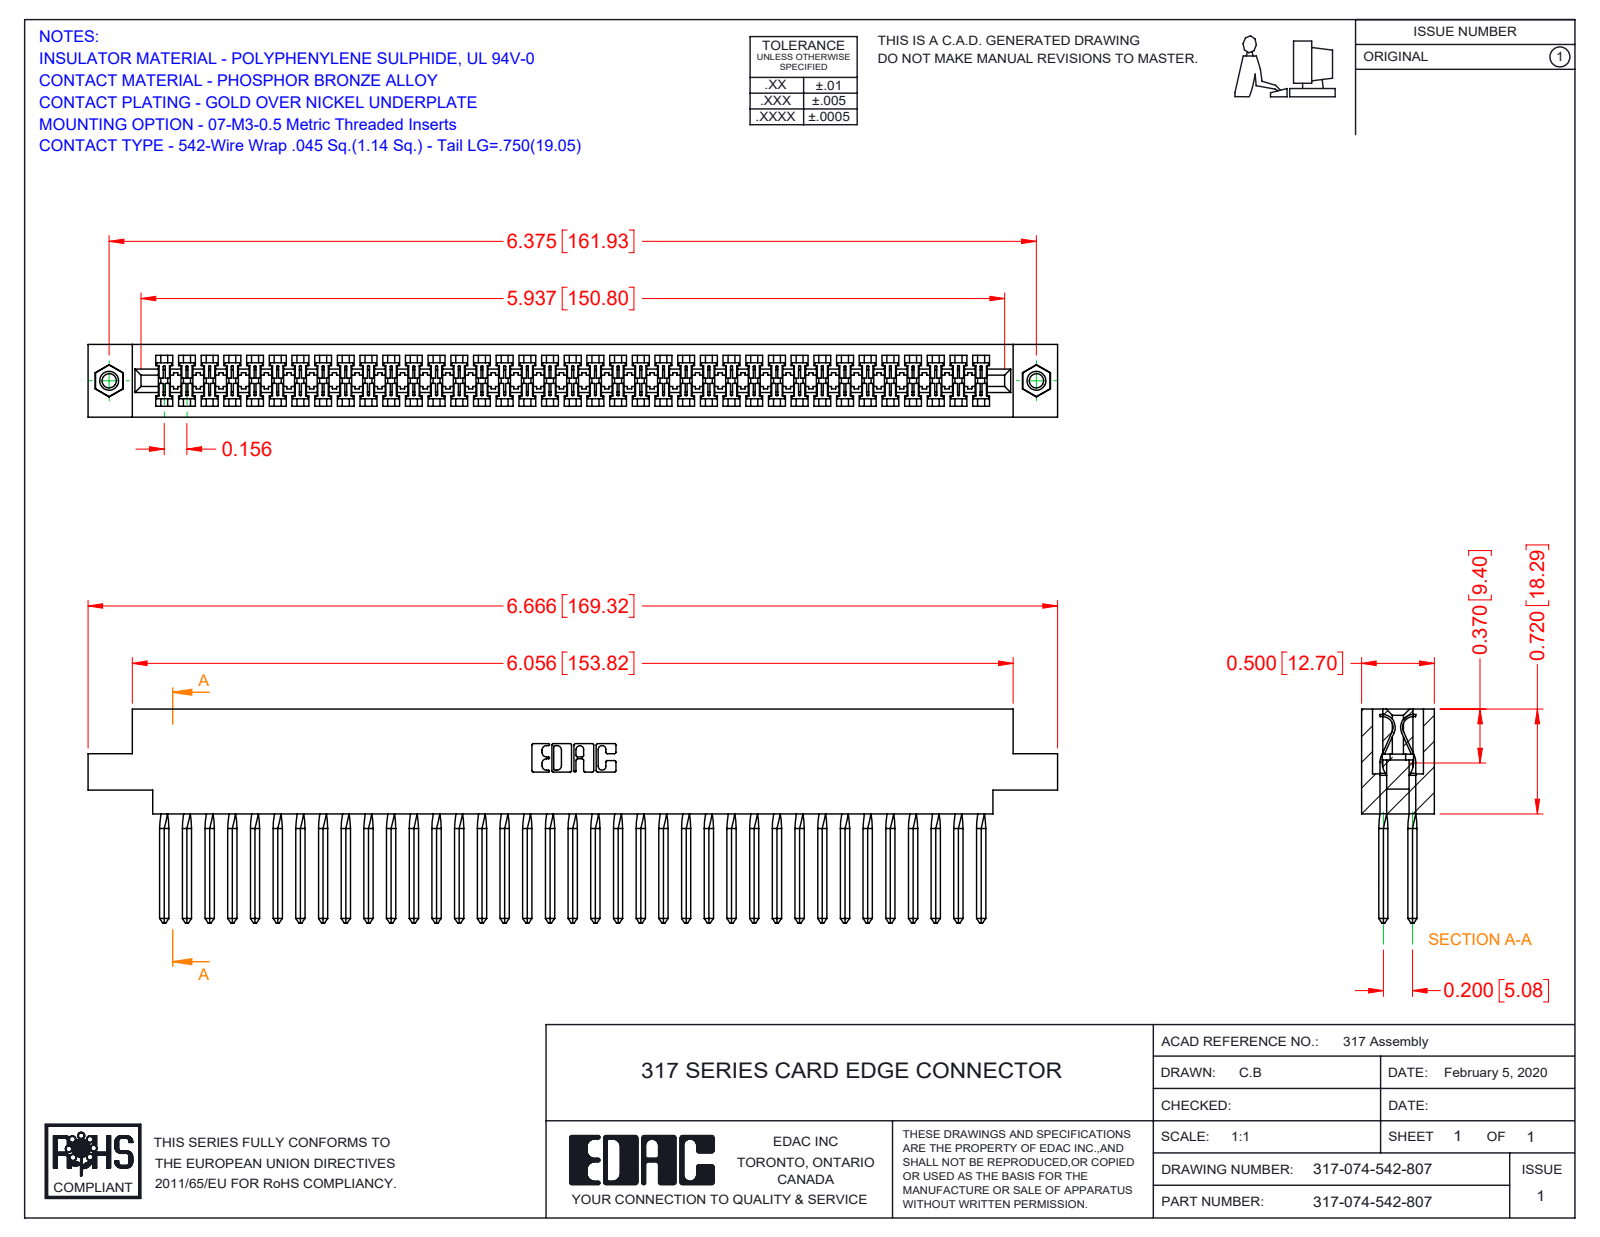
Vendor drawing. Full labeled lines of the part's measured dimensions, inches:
Part name (STEP PRODUCT): 317 Part_.156 Dia - TI; 317-290-003_542; 317-074-542-807; 345-250-001_345-250-005-103
STEP written by: SolidWorks 2016 (CONFIG_CONTROL_DESIGN)
Units: inches
Bodies: 77 solids, 4380 faces (3494 planar, 574 cylindrical, 312 other)
Overall size (bounding box): 6.666 × 1.47 × 0.5
Volume: 1.681 in³ · Surface area: 59.2 in²
Round holes (diameter × count): ⌀0.098 ×2, ⌀0.125 ×2, ⌀0.156 ×2
Round bosses / shafts (diameter × count): ⌀0.155 ×2
Partial cylindrical surfaces — rounded edges, fillets, slot ends (radius × count): R0.006 ×148, R0.01 ×22, R0.007 ×6, R0.031 ×6, R0.026 ×3, R0.074 ×2, R0.089 ×2, R0.1 ×2
Main face-to-face distances: 0.5, 0.075, 0.425, 0.35, 0.2, 0.046, 0.128, 0.372, 0.052, 0.297
Hole centre spacings: 6.375
